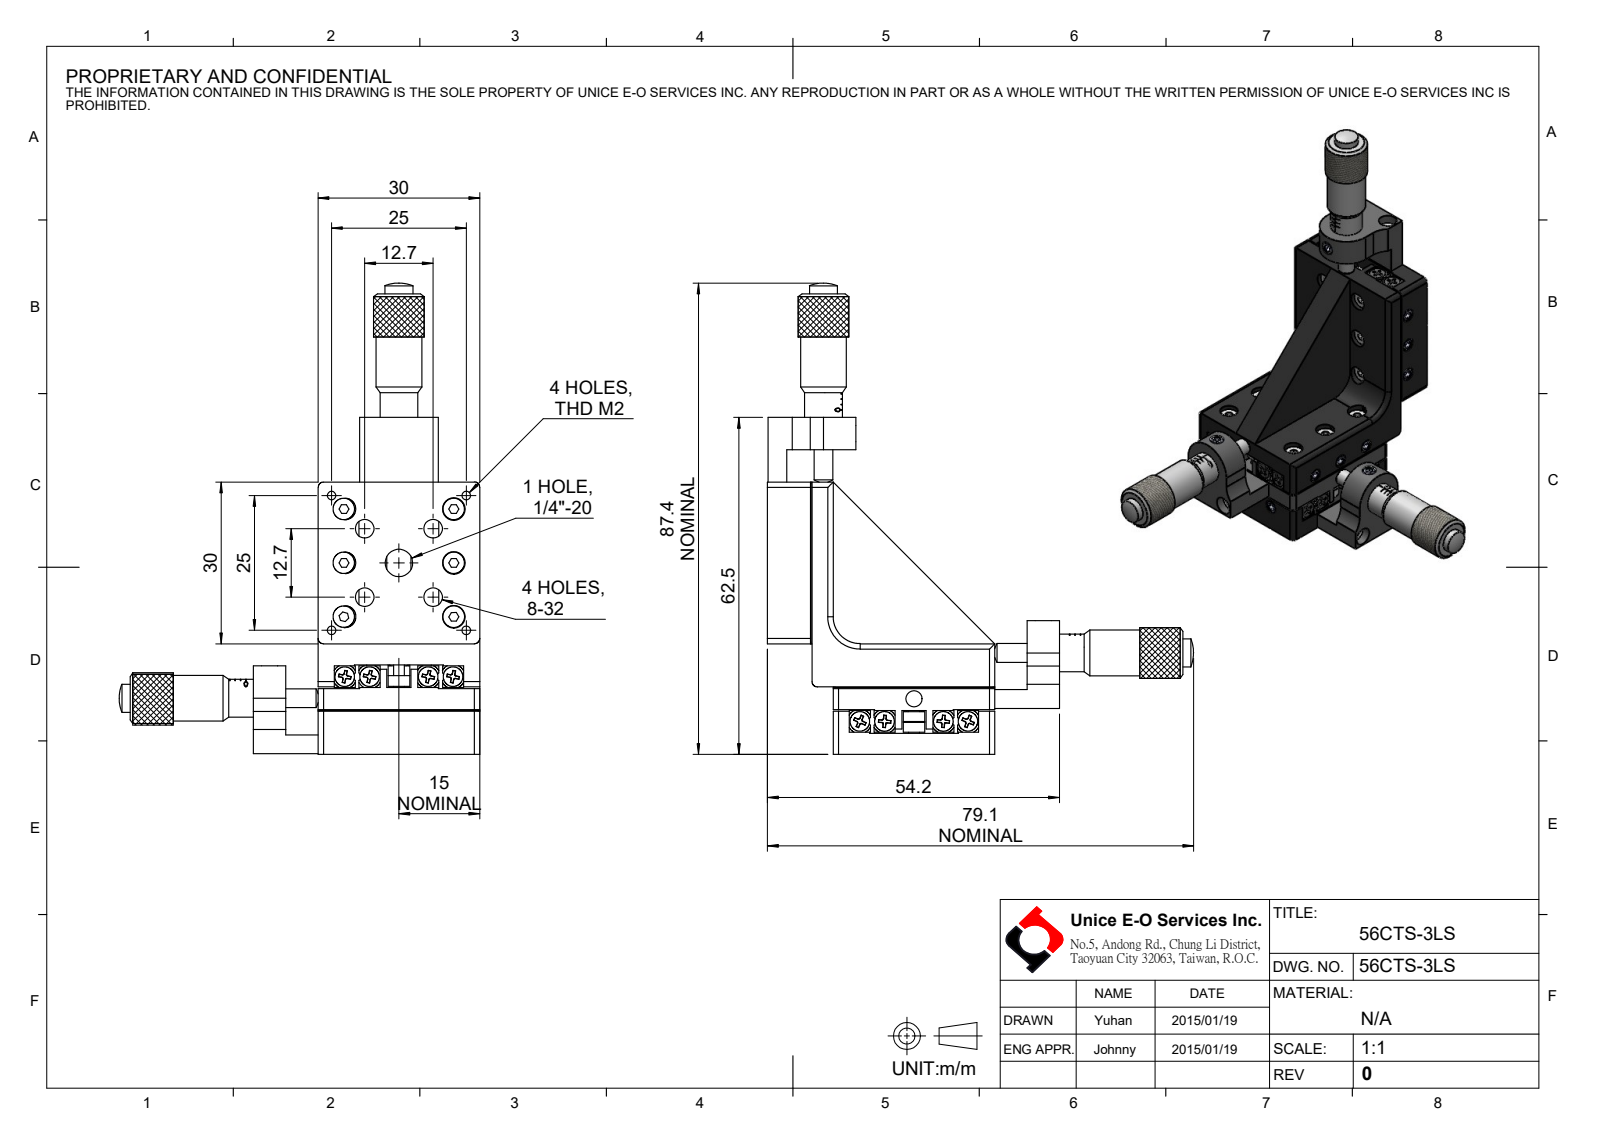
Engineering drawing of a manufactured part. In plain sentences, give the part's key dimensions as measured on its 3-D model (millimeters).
The part is named "56CTS-3LS". Its 3-D file was written by "SolidWorks 2016 (CONFIG_CONTROL_DESIGN)". It is 100 solids with 2710 faces: 1550 planar, 767 cylindrical and 393 other. Overall it measures 87.4 by 79.1 by 66.9 millimeters. Its volume is 36 256 cubic millimeters and its surface area 38 169 square millimeters. Round holes: 68 of diameter 1.6, 34 of diameter 4, 12 of diameter 2.4, 12 of diameter 2.5, 9 of diameter 2.2, 8 of diameter 3.45, 6 of diameter 2.1, 6 of diameter 2.6, 6 of diameter 4.2, 3 of diameter 3, 3 of diameter 3.5, 3 of diameter 6. Round bosses or shafts: 35 of diameter 2, 13 of diameter 4, 12 of diameter 3.6, 12 of diameter 3, 12 of diameter 1.95, 3 of diameter 9.4, 3 of diameter 8.5, 3 of diameter 7. Partial cylindrical surfaces (rounded edges, fillets, slot ends): 17 of radius 1.25, 13 of radius 1, 8 of radius 2, 7 of radius 5, 3 of radius 6. The main face-to-face distances are 4.1, 8.3, 3.9, 8.1, 4.2, 4, 8.5, 4.4, 3, 30. The hole center spacings are 15.5, 10, 11.14, 18.45, 4.9, 19.83, 25.3, 16.8.
